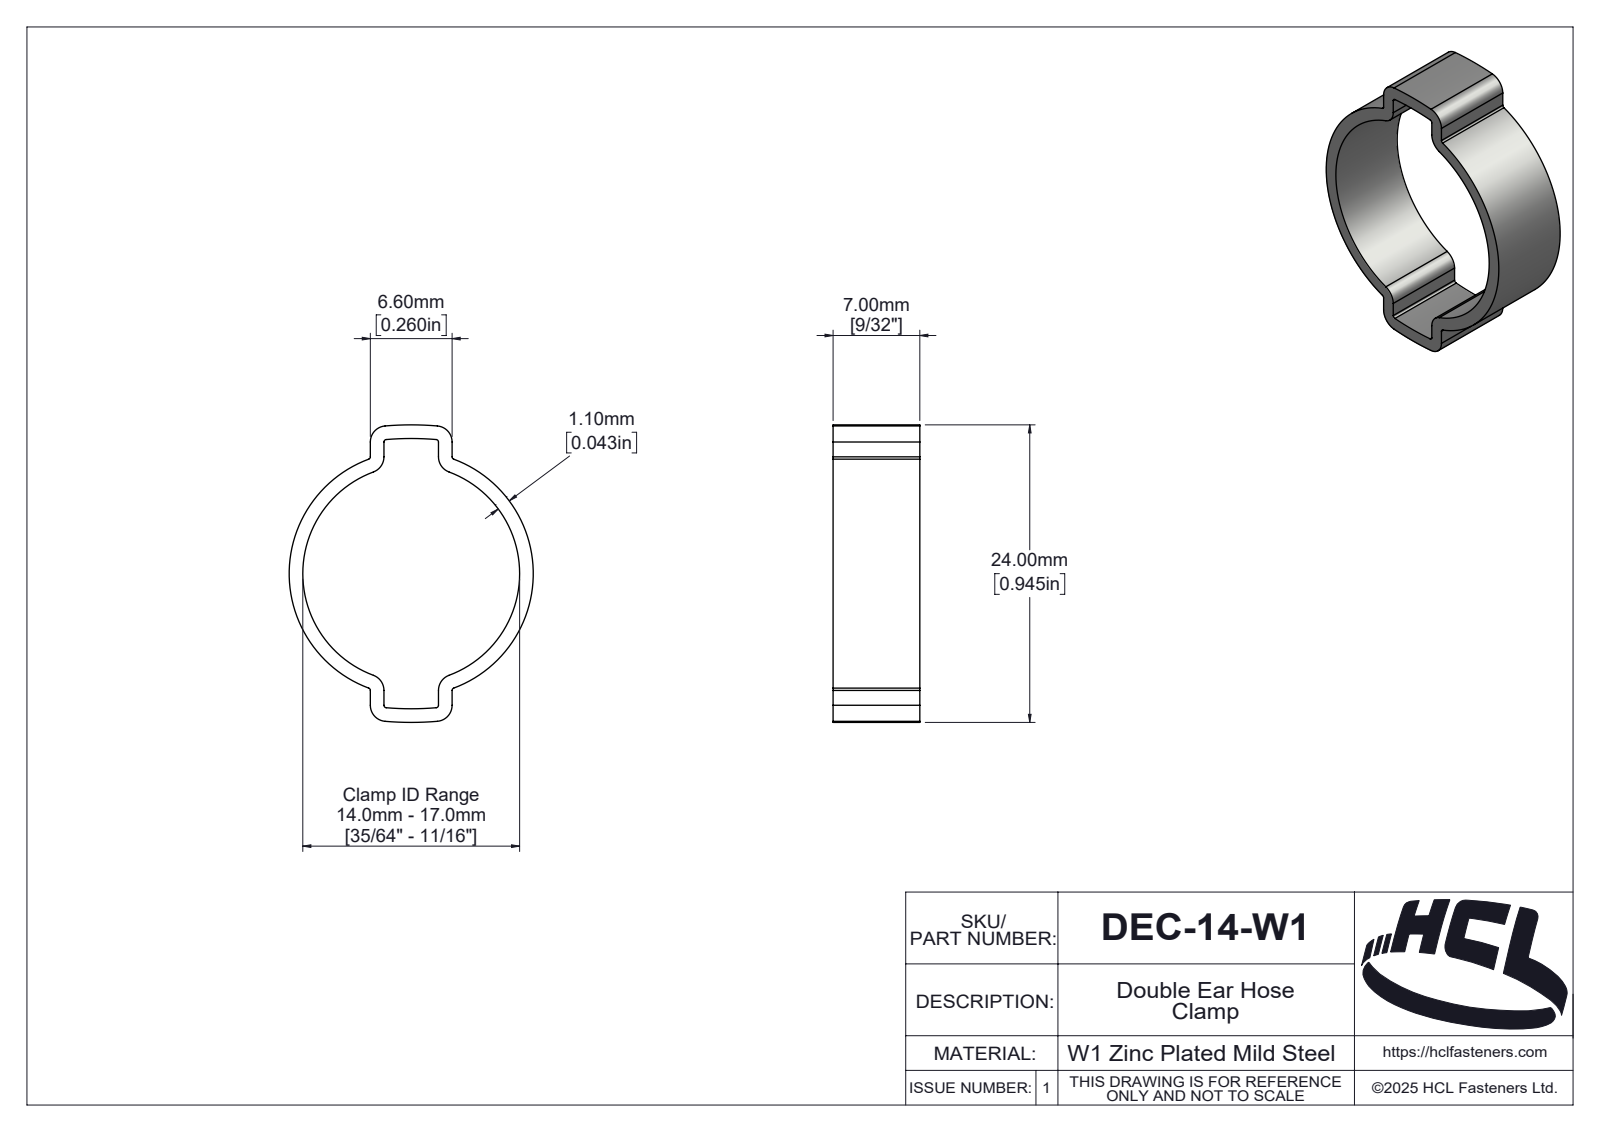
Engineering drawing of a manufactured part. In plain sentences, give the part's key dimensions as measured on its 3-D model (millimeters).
The part is named "DEC-14-W1". Its 3-D file was written by "SolidWorks 2025 (AUTOMOTIVE_DESIGN)". It is 1 solid with 137 faces: 12 planar, 76 cylindrical and 49 other. Overall it measures 24 by 19.7 by 7 millimeters. Its volume is 511 cubic millimeters and its surface area 1 077 square millimeters. Partial cylindrical surfaces (rounded edges, fillets, slot ends): 8 of radius 0.2, 8 of radius 1.3, 2 of radius 24.25, 2 of radius 25.35, 1 of radius 0.13, 1 of radius 0.54, 1 of radius 0.67, 1 of radius 0.71. The main face-to-face distances are 7, 1.1, 5.5, 6.6, 4.4, 3.12, 2.02, 2.38, 3.48, 3.22.
